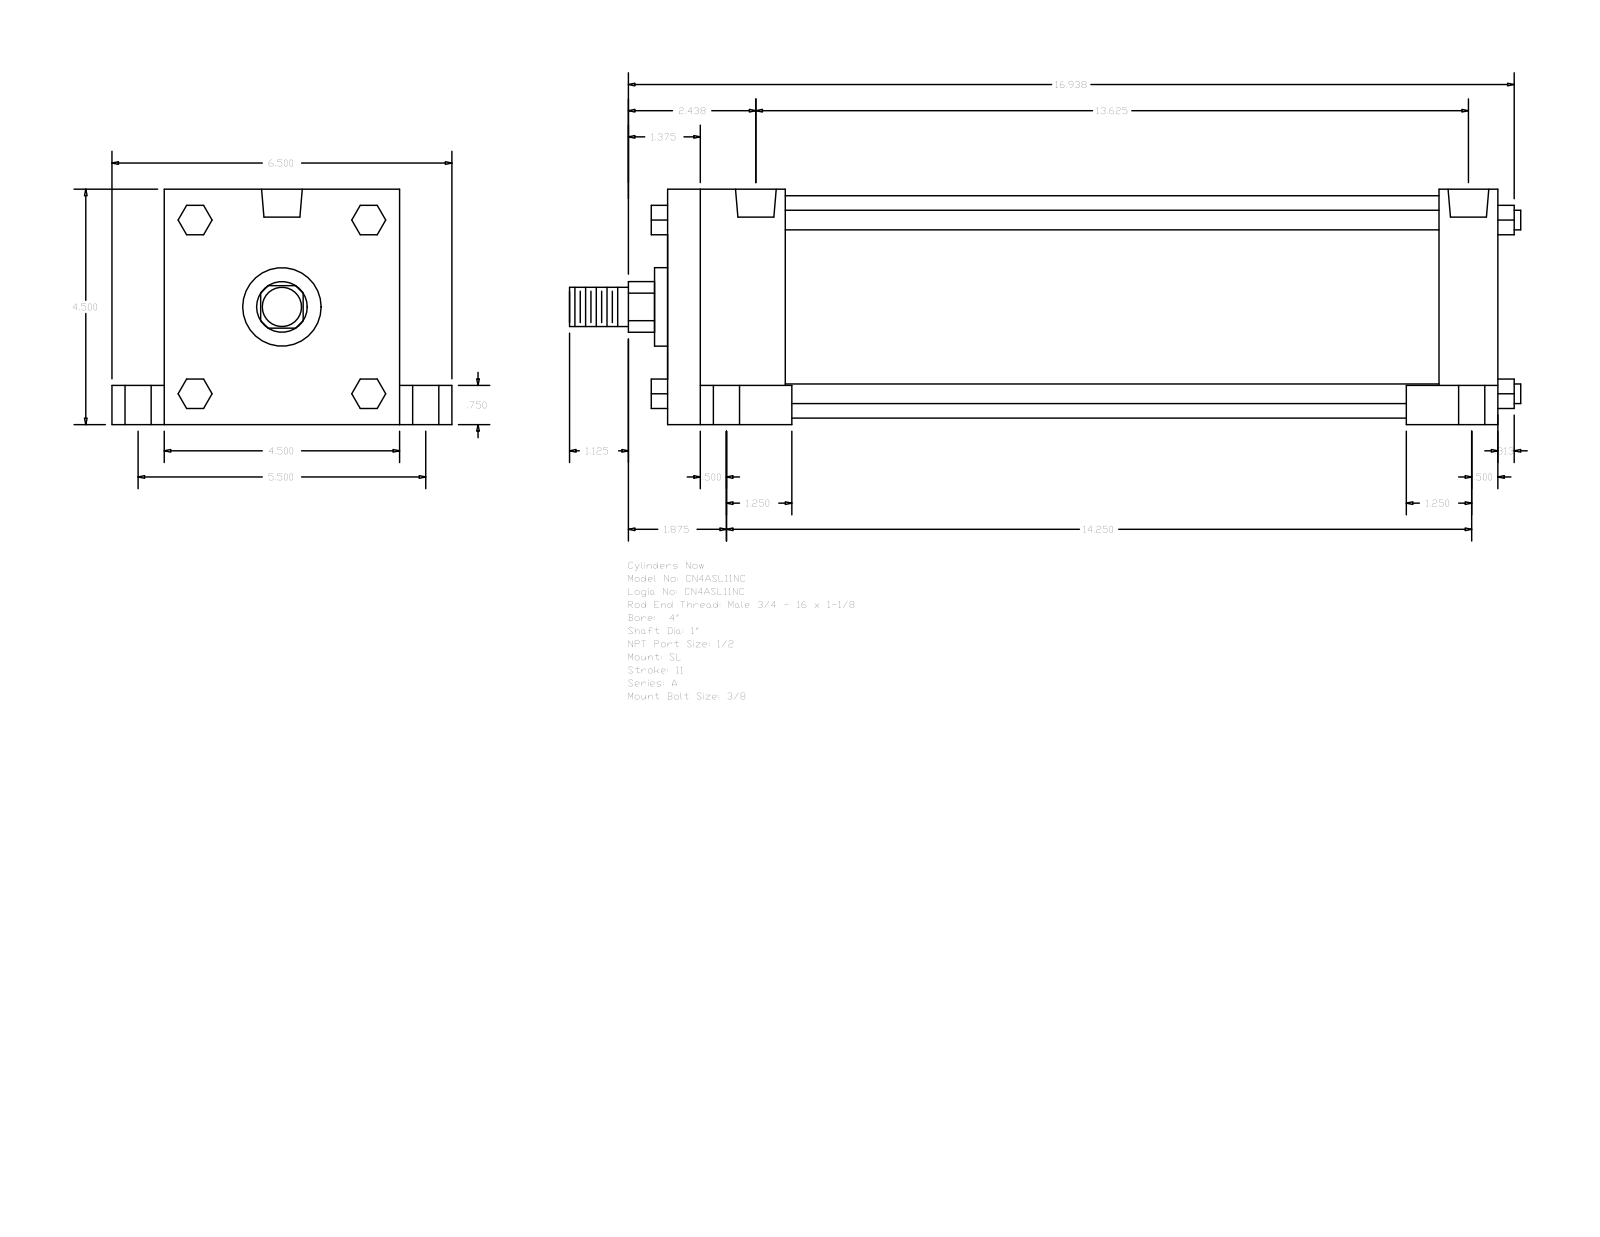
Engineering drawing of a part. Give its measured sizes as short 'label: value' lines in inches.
name: A_SL__0400_1
written by: GSSL Pune (CONFIG_CONTROL_DESIGN)
unit: in
bodies: 0 solids, 150 faces (114 planar, 36 cylindrical, 0 other)
size: 18.187 × 6.5 × 4.5
holes: 4× ⌀0.344, 4× ⌀0.5, 4× ⌀0.75, 2× ⌀0.778
bosses: 4× ⌀0.375, 1× ⌀4.25, 1× ⌀1.5, 1× ⌀1, 1× ⌀0.75
rounds: 1× R0.484
face distances: 4.5, 15.875, 1.125, 2.25, 13.625, 14.75, 12.5, 0.75, 1, 5.5
hole spacings: 0.125, 2.751, 2.756, 2.807, 2.835, 5.5, 13.375, 13.5
